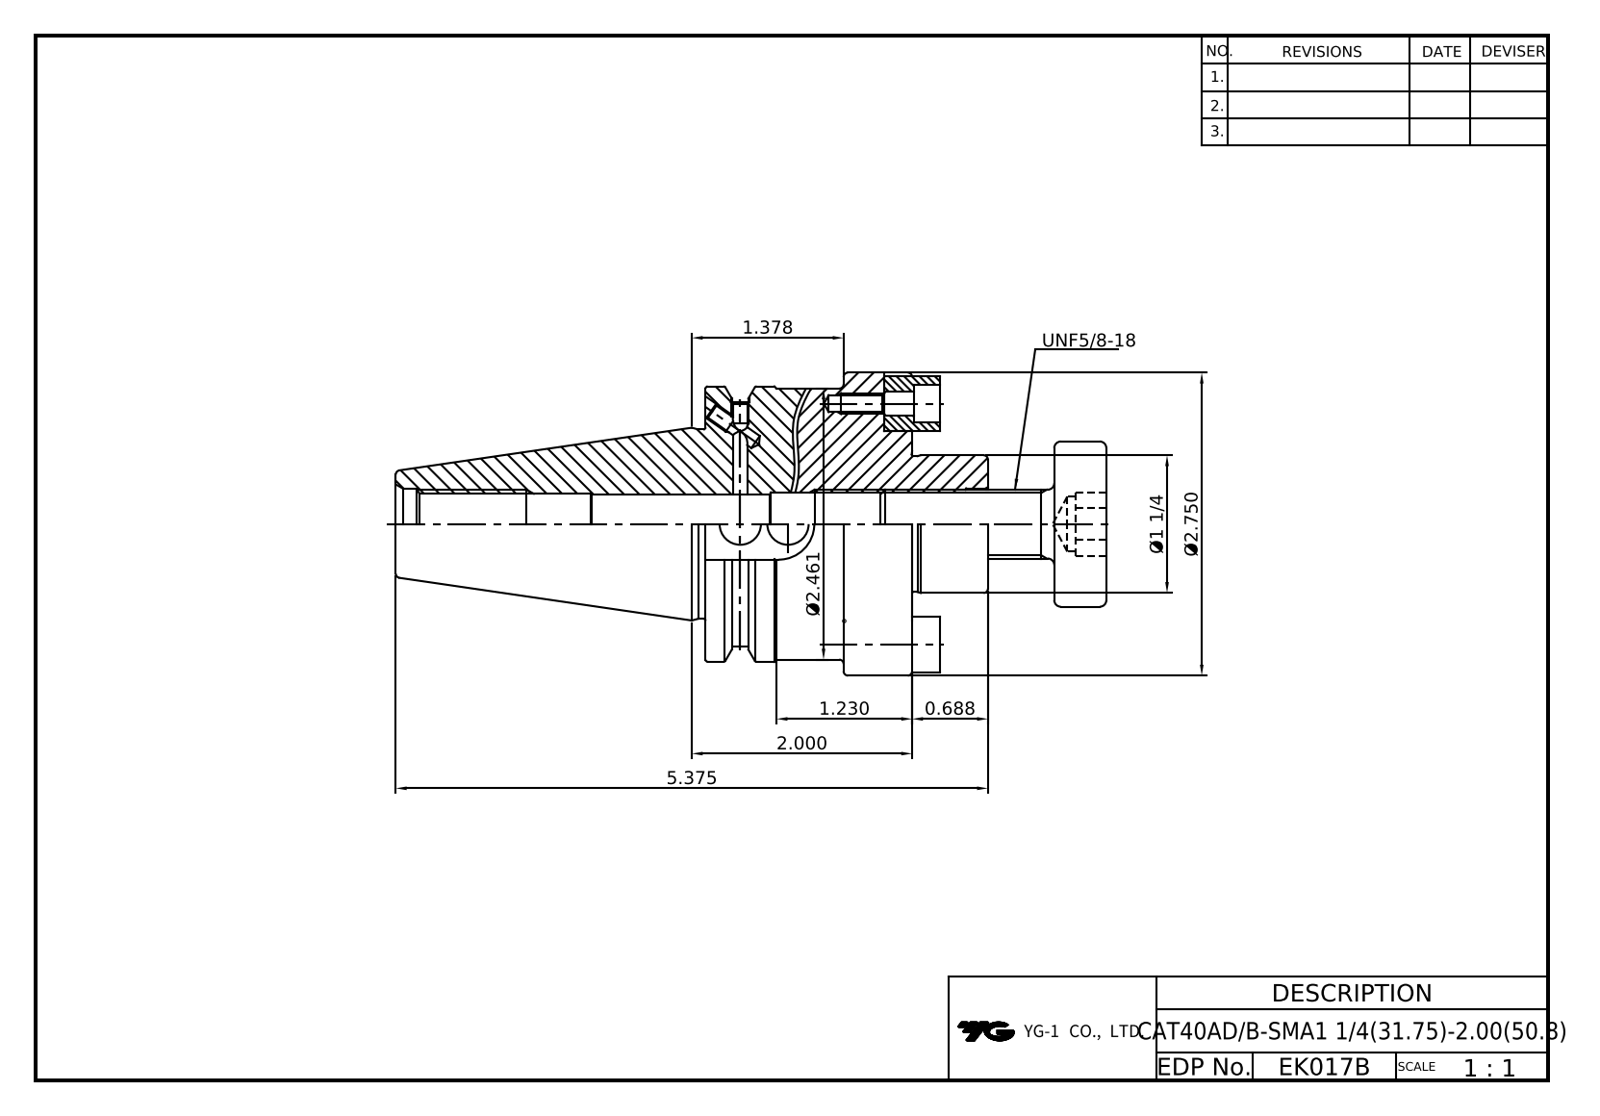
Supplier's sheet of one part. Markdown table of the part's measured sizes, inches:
| quantity | value |
| --- | --- |
| part name | LO-CAT40ADB-SMA31.75-50.8; HEX'' WRENCH BOLT-UNC#10-24x1_2L; DRIVE KEY-12.7x12.7x12.7; COLLAR BOLT-UNF5_8-18x40L |
| STEP written by | Autodesk Inventor 2022 (AUTOMOTIVE_DESIGN) |
| units | inches |
| bodies | 6 solids, 173 faces (84 planar, 49 cylindrical, 40 other) |
| overall size | 6.481 × 2.75 × 2.75 |
| volume | 14.35 in³ |
| surface area | 66.38 in² |
| round holes (diameter × count) | 0.128 × 4, 0.145 × 2, 0.157 × 2, 0.165 × 2, 0.217 × 2, 0.343 × 2, 0.375 × 1, 0.5 × 1, 0.512 × 1, 0.527 × 1, 0.565 × 1, 0.642 × 1 |
| round bosses / shafts (diameter × count) | 0.312 × 2, 0.19 × 2, 2.75 × 1, 2.5 × 1, 2.461 × 1, 1.717 × 1, 1.5 × 1, 1.25 × 1 |
| partial cylindrical surfaces (radius × count) | 0.25 × 2, 0.322 × 1, 1.108 × 1 |
| main face-to-face distances | 1.875, 3.669, 1.794, 3.197, 1.322, 0.472, 0.25, 0.5, 1.253, 0.622 |
| hole center spacings | 1.093, 1.094, 2.187, 2.187, 2.187 |
